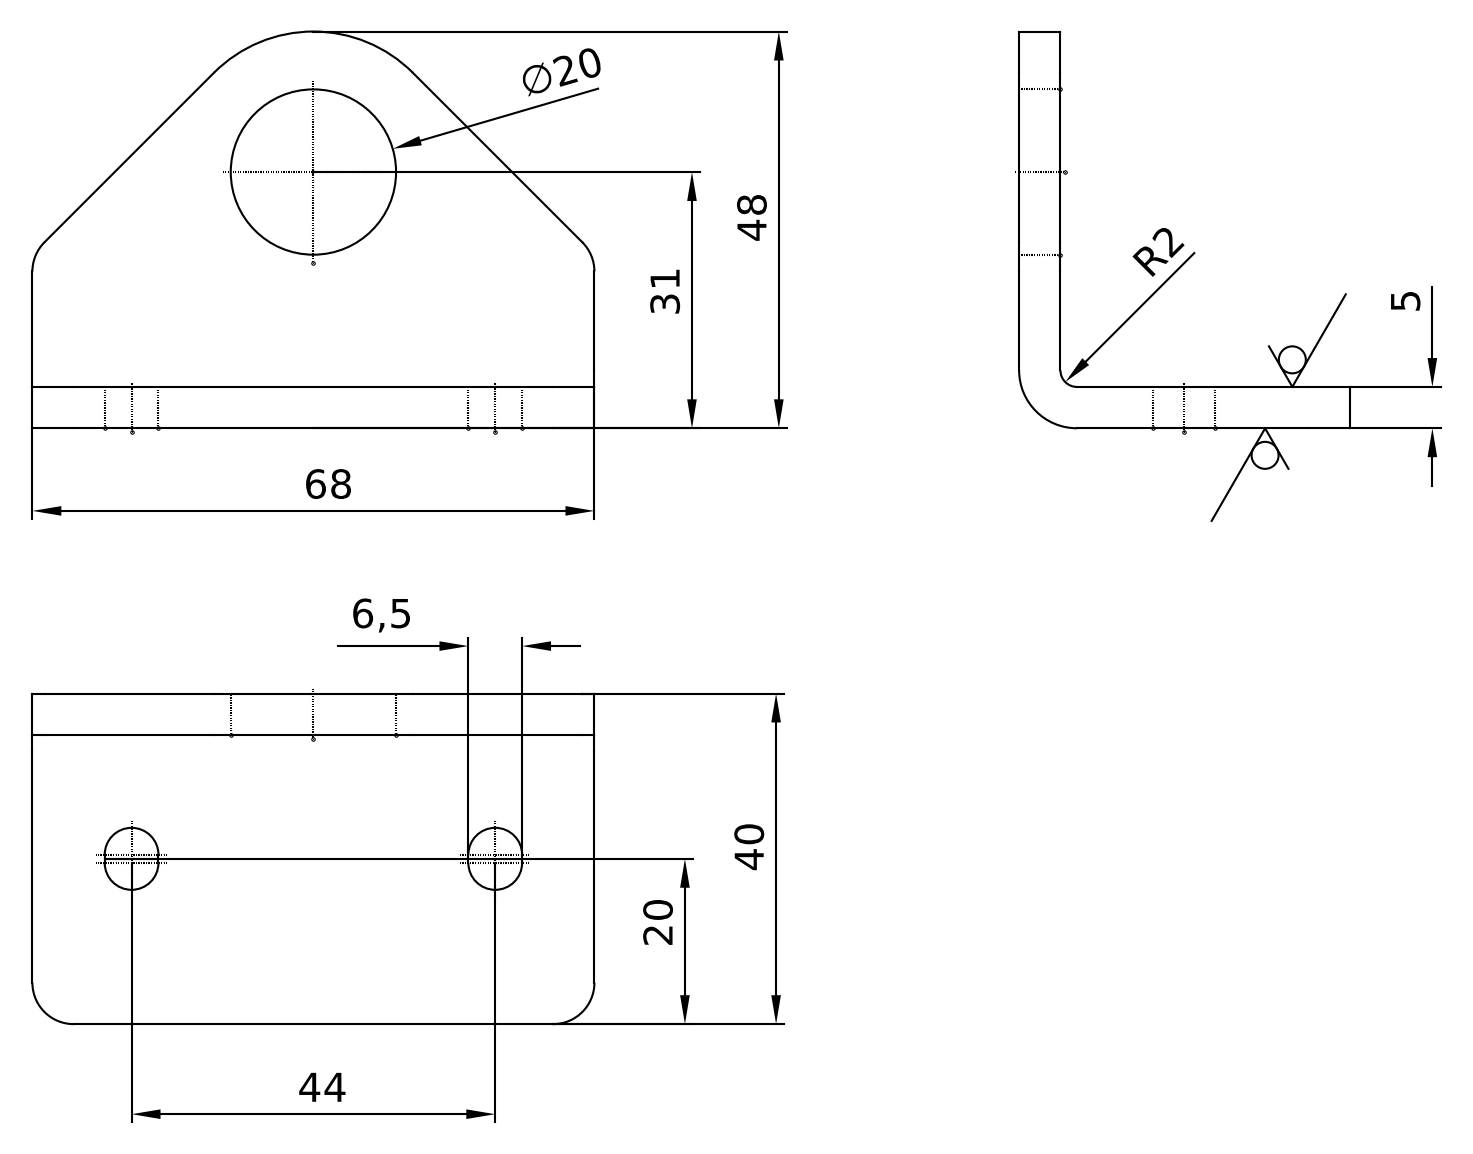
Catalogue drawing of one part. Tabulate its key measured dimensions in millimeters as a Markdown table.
| quantity | value |
| --- | --- |
| part name | 800 061 |
| STEP written by | Autodesk Inventor 2024 (AUTOMOTIVE_DESIGN) |
| units | millimeters |
| bodies | 1 solid, 29 faces (17 planar, 12 cylindrical, 0 other) |
| overall size | 68 × 48 × 40 |
| volume | 21 841 mm³ |
| surface area | 10 576 mm² |
| round holes (diameter × count) | 20 × 1 |
| partial cylindrical surfaces (radius × count) | 3.25 × 4, 5 × 4, 2 × 1, 7 × 1, 17 × 1 |
| main face-to-face distances | 5, 40, 35, 68, 8.75, 15.25, 52.75, 59.25, 44, 6.5 |
